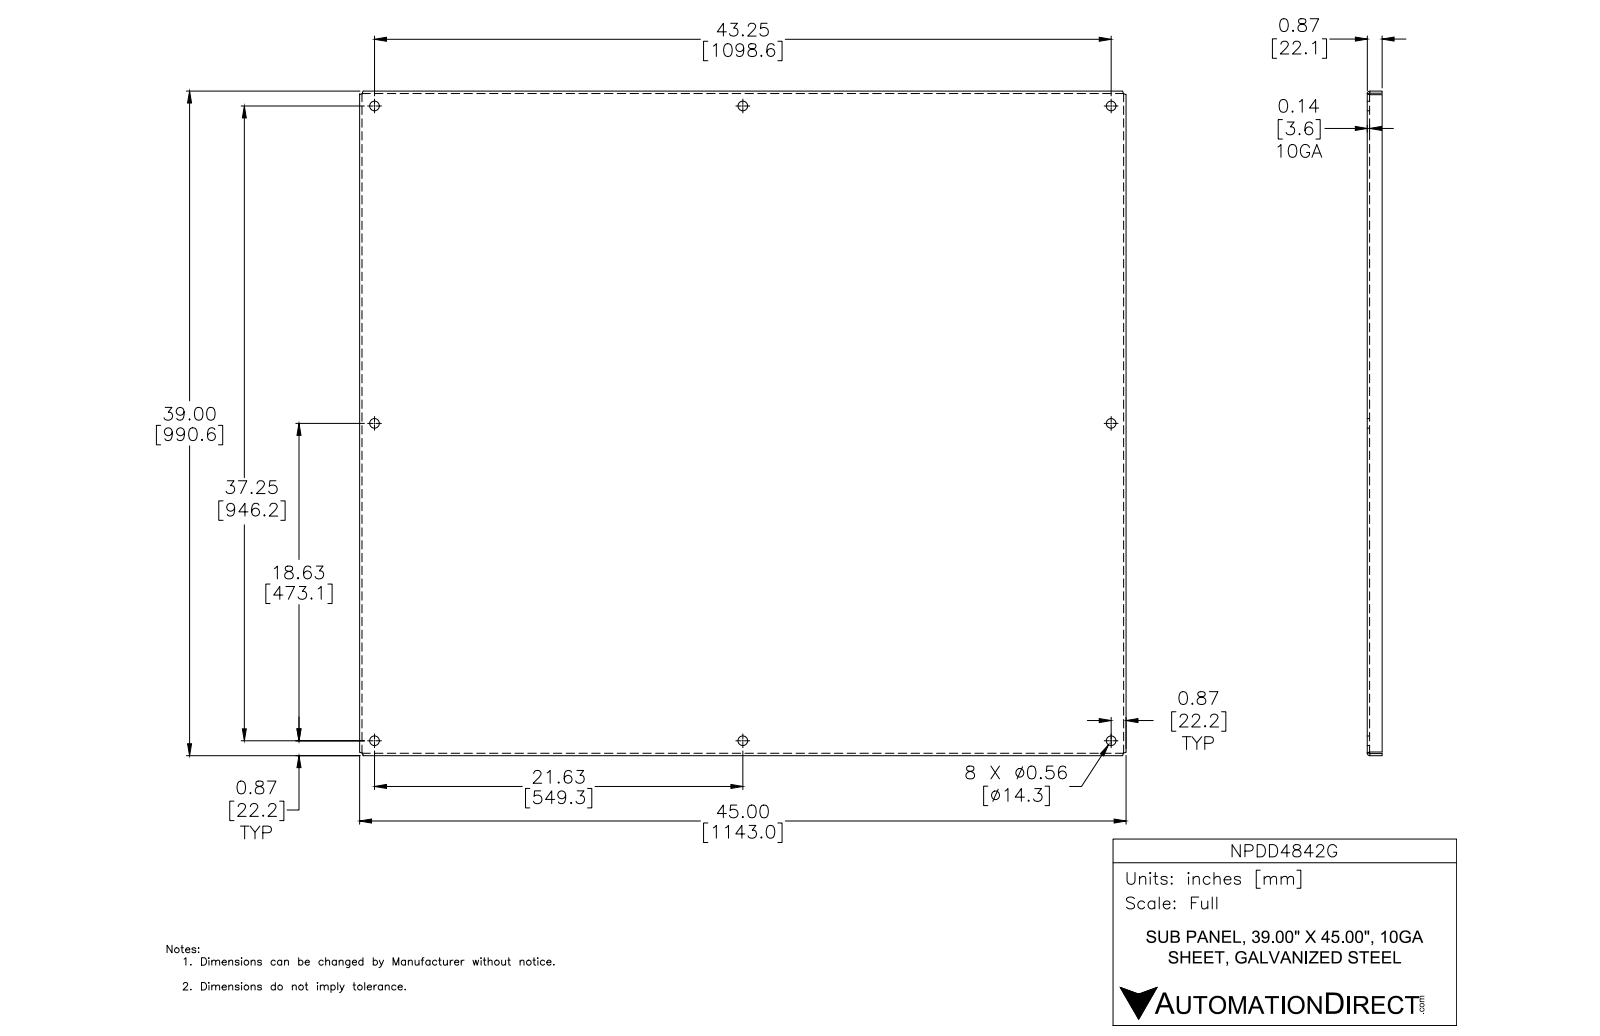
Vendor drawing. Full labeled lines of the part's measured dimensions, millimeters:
Part name (STEP PRODUCT): NPDD4242G-NPDD7272G
STEP written by: Autodesk Inventor 2012 (AUTOMOTIVE_DESIGN)
Units: millimetres
Bodies: 1 solid, 46 faces (22 planar, 16 cylindrical, 8 other)
Overall size (bounding box): 1143 × 990.6 × 22.2
Volume: 3 833 000 mm³ · Surface area: 2 429 000 mm²
Round holes (diameter × count): ⌀14.3 ×8
Partial cylindrical surfaces — rounded edges, fillets, slot ends (radius × count): R0.8 ×4, R4 ×4
Main face-to-face distances: 3.2, 3.2, 990.6, 987.4, 987.4, 984.3, 1139.8, 1143, 1136.7, 1139.8
Hole centre spacings: 473.1, 724.9, 1094, 1196.1, 946.2, 1098.6, 549.3, 549.3
